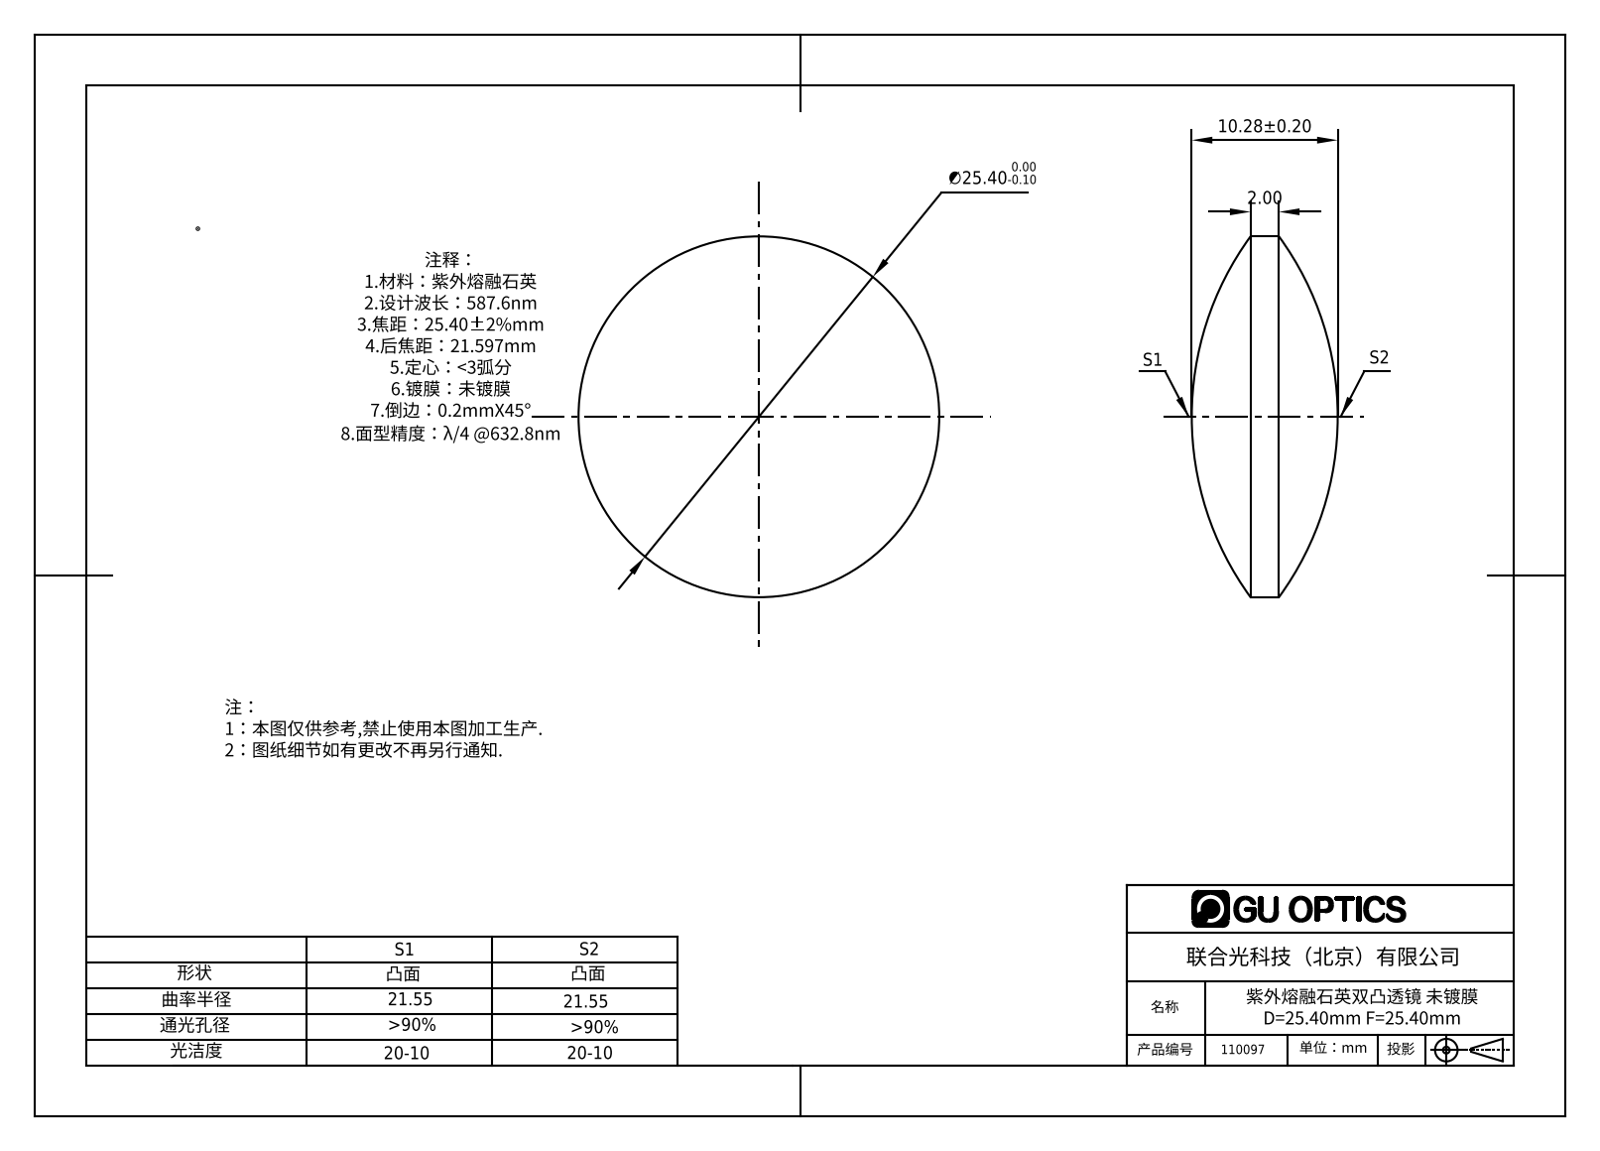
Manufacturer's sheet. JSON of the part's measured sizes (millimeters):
{"part_name": "110097", "step_written_by": "SolidWorks 2016 (CONFIG_CONTROL_DESIGN)", "units": "millimeters", "bodies": {"solids": 1, "faces": 6, "planar": 0, "cylindrical": 2, "other": 4}, "overall_size": [25.4, 25.4, 10.28], "volume_mm3": 3185, "surface_area_mm2": 1281, "round_bosses_or_shafts": [[25.4, 1]]}
